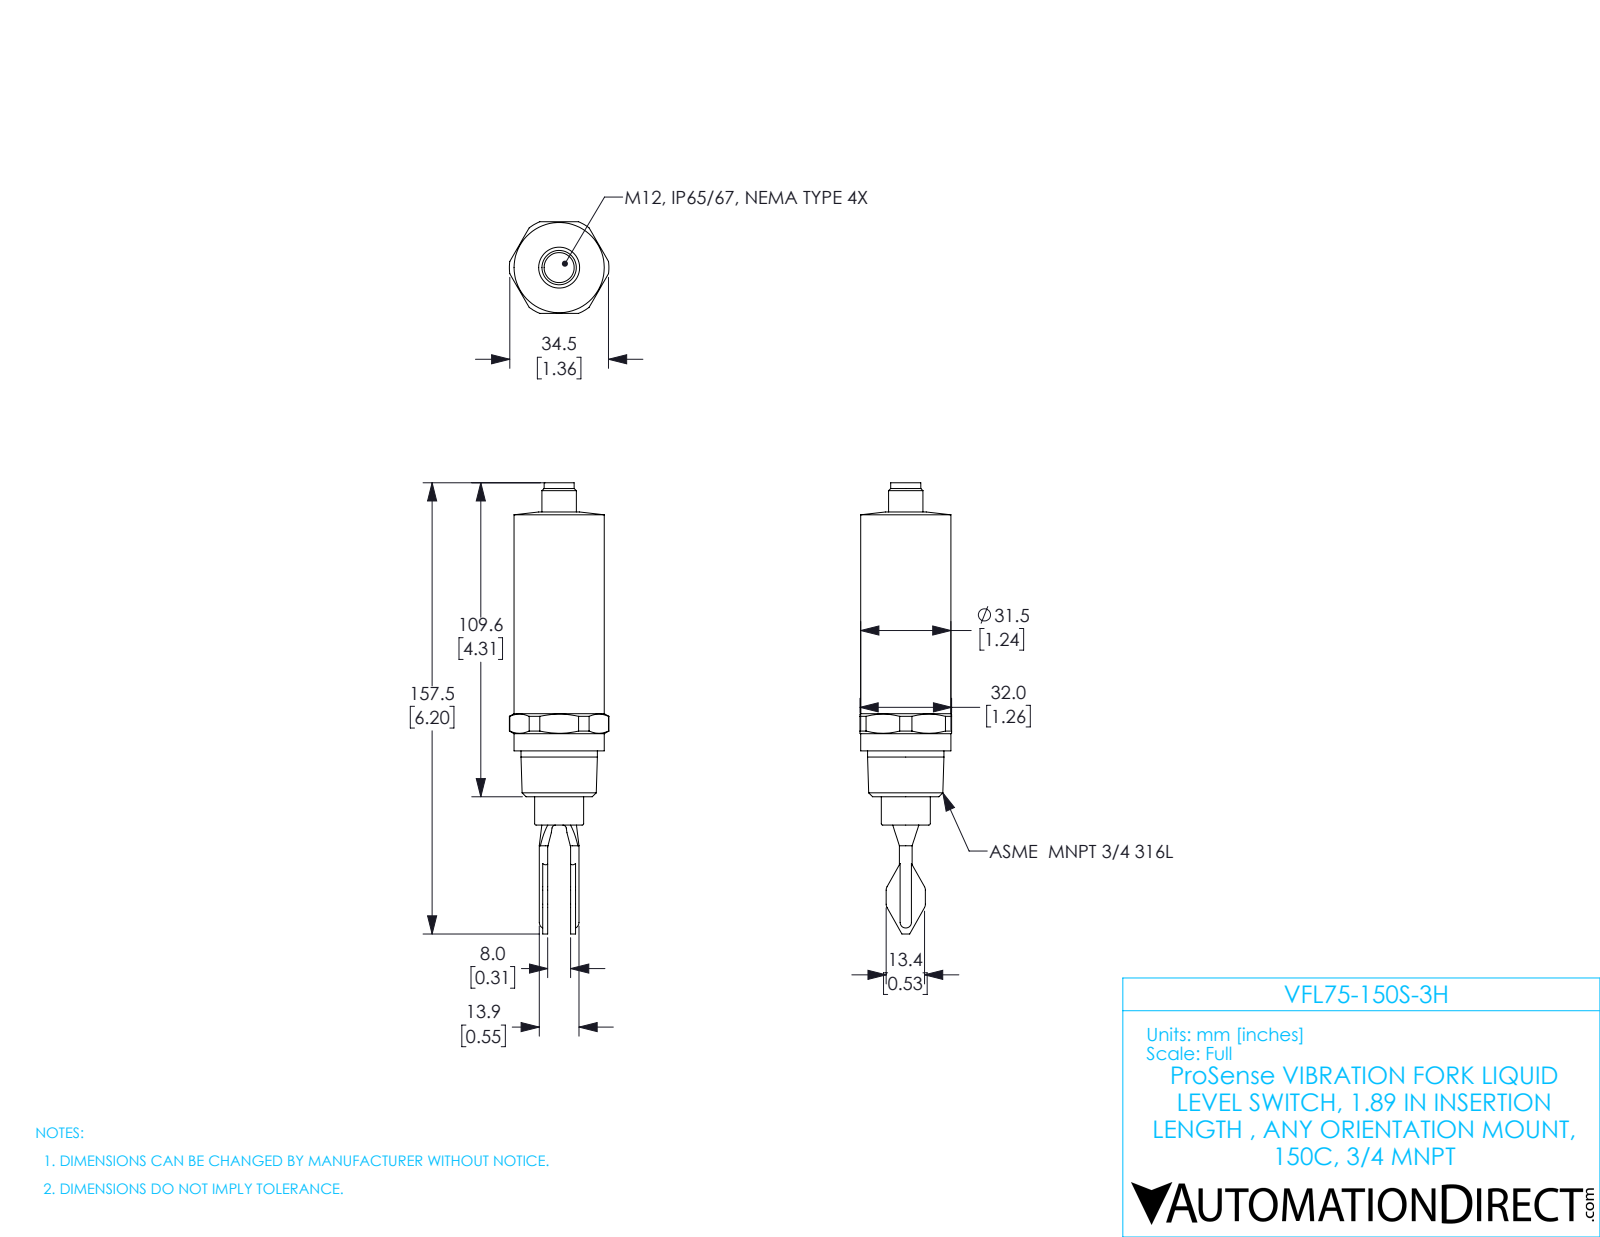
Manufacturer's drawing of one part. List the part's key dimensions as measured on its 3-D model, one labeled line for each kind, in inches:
Part name (STEP PRODUCT): VFL75-150S-3H
STEP written by: SolidWorks 2017 (AUTOMOTIVE_DESIGN)
Units: inches
Bodies: 1 solid, 98 faces (45 planar, 34 cylindrical, 19 other)
Overall size (bounding box): 6.201 × 1.368 × 1.26
Volume: 4.799 in³ · Surface area: 21.01 in²
Round bosses / shafts (diameter × count): ⌀1.24 ×1, ⌀1.05 ×1, ⌀0.673 ×1, ⌀0.472 ×1, ⌀0.413 ×1
Partial cylindrical surfaces — rounded edges, fillets, slot ends (radius × count): R0.047 ×4, R0.094 ×4, R0.088 ×2, R0.684 ×1
Main face-to-face distances: 0.068, 0.383, 0.315, 1.26, 0.63, 0.451, 0.39, 1.02, 4.705, 4.315
